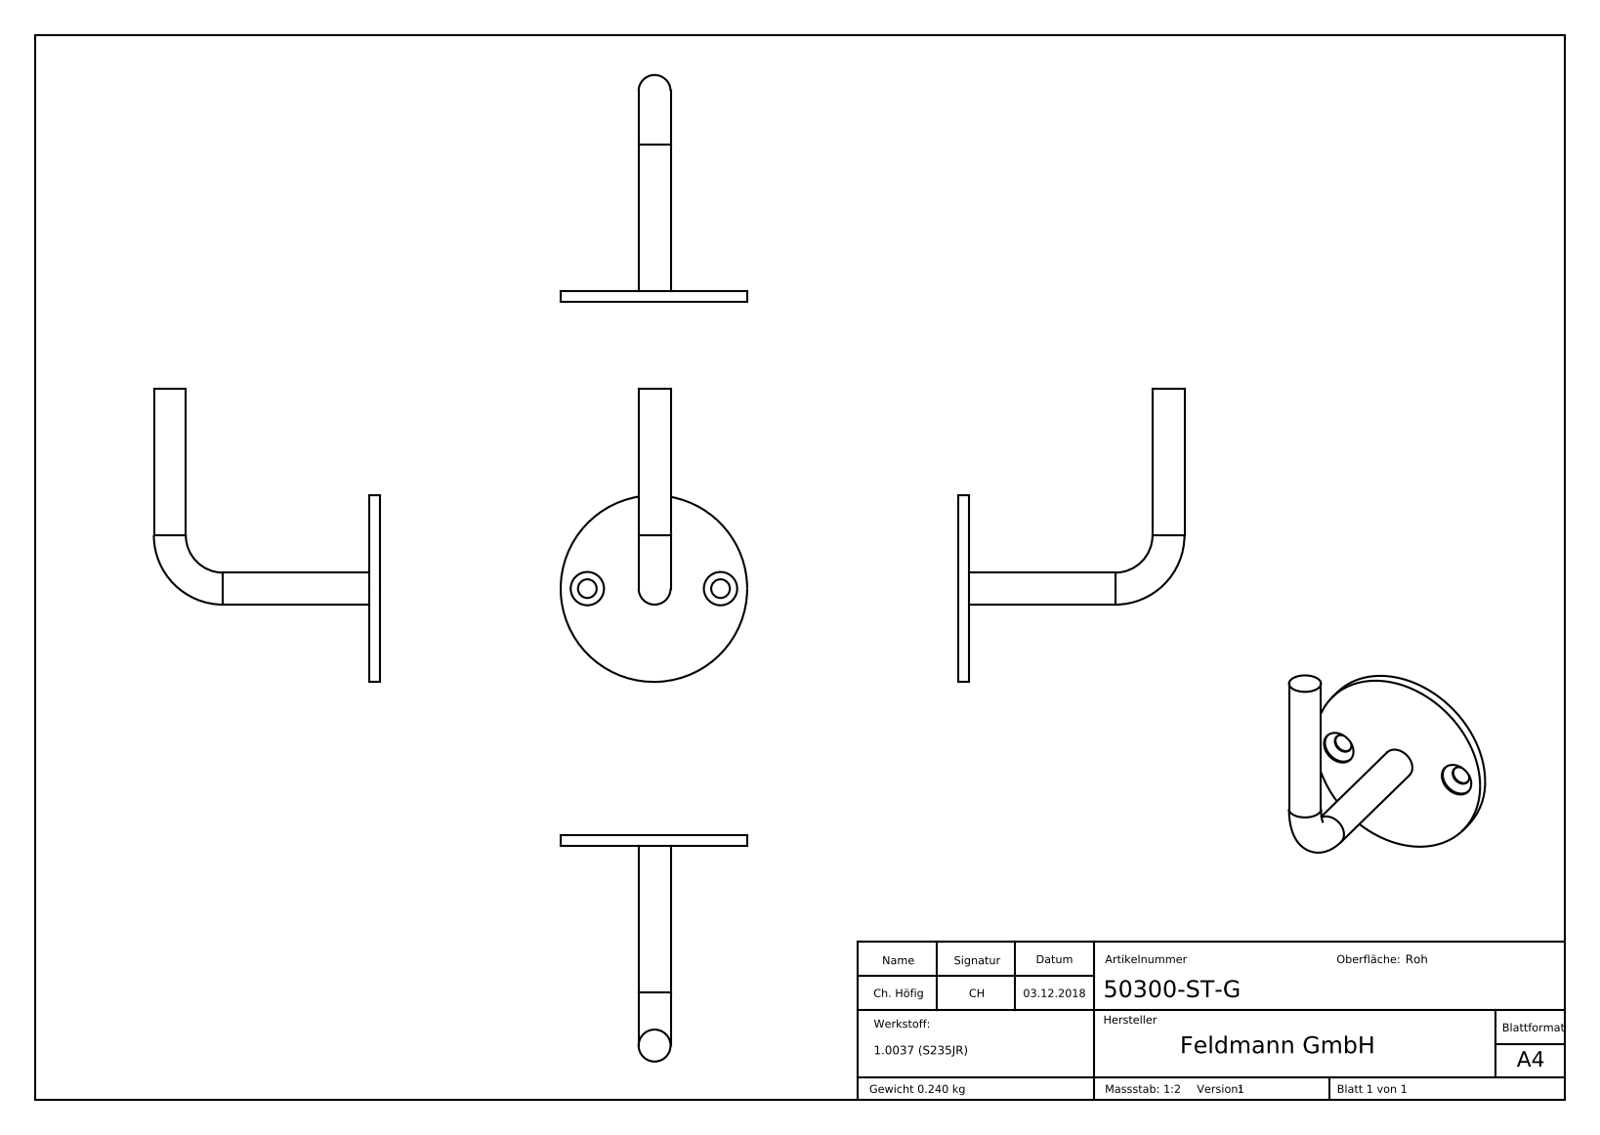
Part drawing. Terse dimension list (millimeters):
name: 50300-ST-G
written by: SolidWorks 2015 (CONFIG_CONTROL_DESIGN)
unit: mm
bodies: 1 solid, 253 faces (112 planar, 14 cylindrical, 127 other)
size: 110 × 85 × 70
volume: 30 740 mm³; area: 13 954 mm²
holes: 2× ⌀7, 2× ⌀12.5
bosses: 2× ⌀12, 1× ⌀70
face distances: 4, 0.5, 3.5, 0.38, 0.54, 0.67, 0.72, 1.33, 0.85, 0.51
hole spacings: 50
